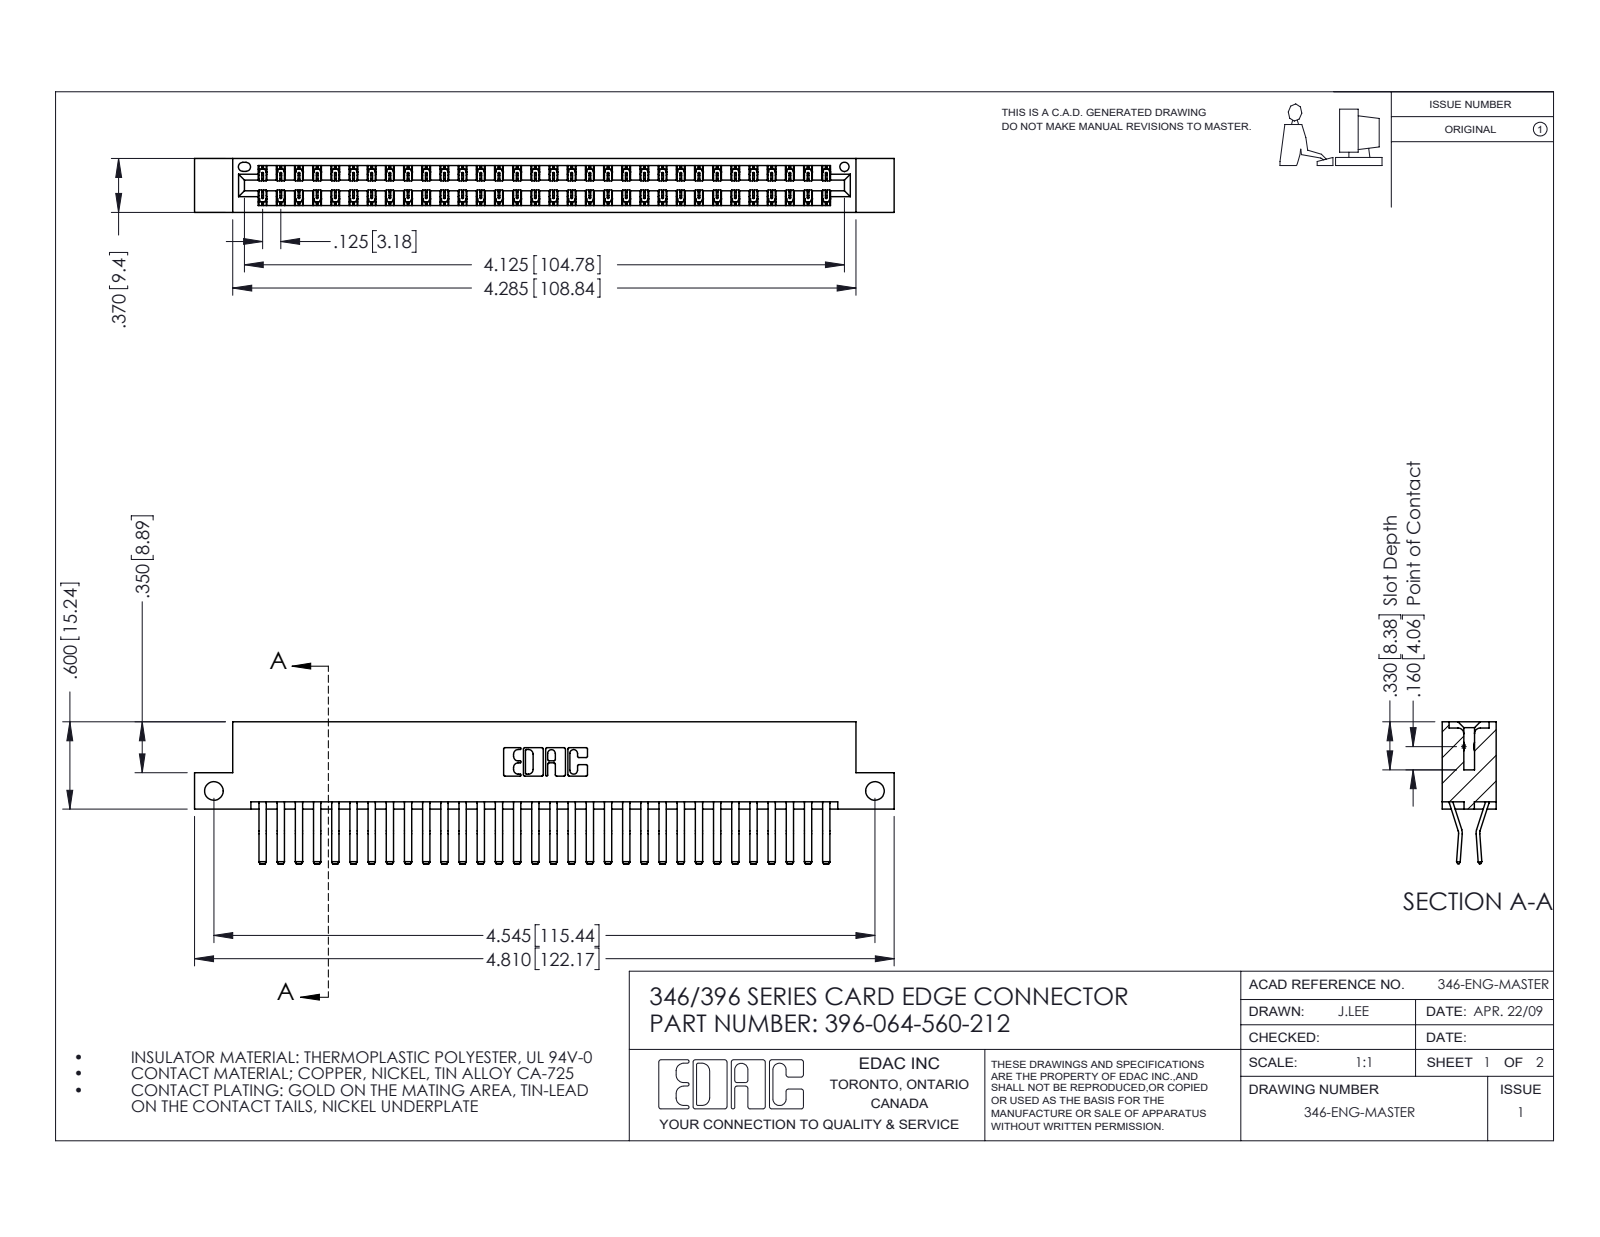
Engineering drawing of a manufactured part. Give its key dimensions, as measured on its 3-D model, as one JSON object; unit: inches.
{"part_name": "396-064-560-212; 346 Part_Flush Mounting Lugs - Side Mount; 345-292-001_560 Tail", "step_written_by": "SolidWorks 2016 (CONFIG_CONTROL_DESIGN)", "units": "inches", "bodies": {"solids": 65, "faces": 3578, "planar": 2316, "cylindrical": 1262, "other": 0}, "overall_size": [4.81, 0.975, 0.37], "volume_in3": 0.743, "surface_area_in2": 27.2, "round_holes": [[0.128, 2], [0.064, 1]], "partial_cylinders_radius": [[0.006, 96], [0.01, 22], [0.007, 6], [0.031, 6], [0.026, 3], [0.01, 2], [0.014, 2], [0.022, 2]], "face_to_face_distances": [0.048, 0.322, 0.37, 0.25, 0.025, 0.072, 0.298, 0.275, 0.148, 0.222], "hole_center_spacings": [4.545]}
